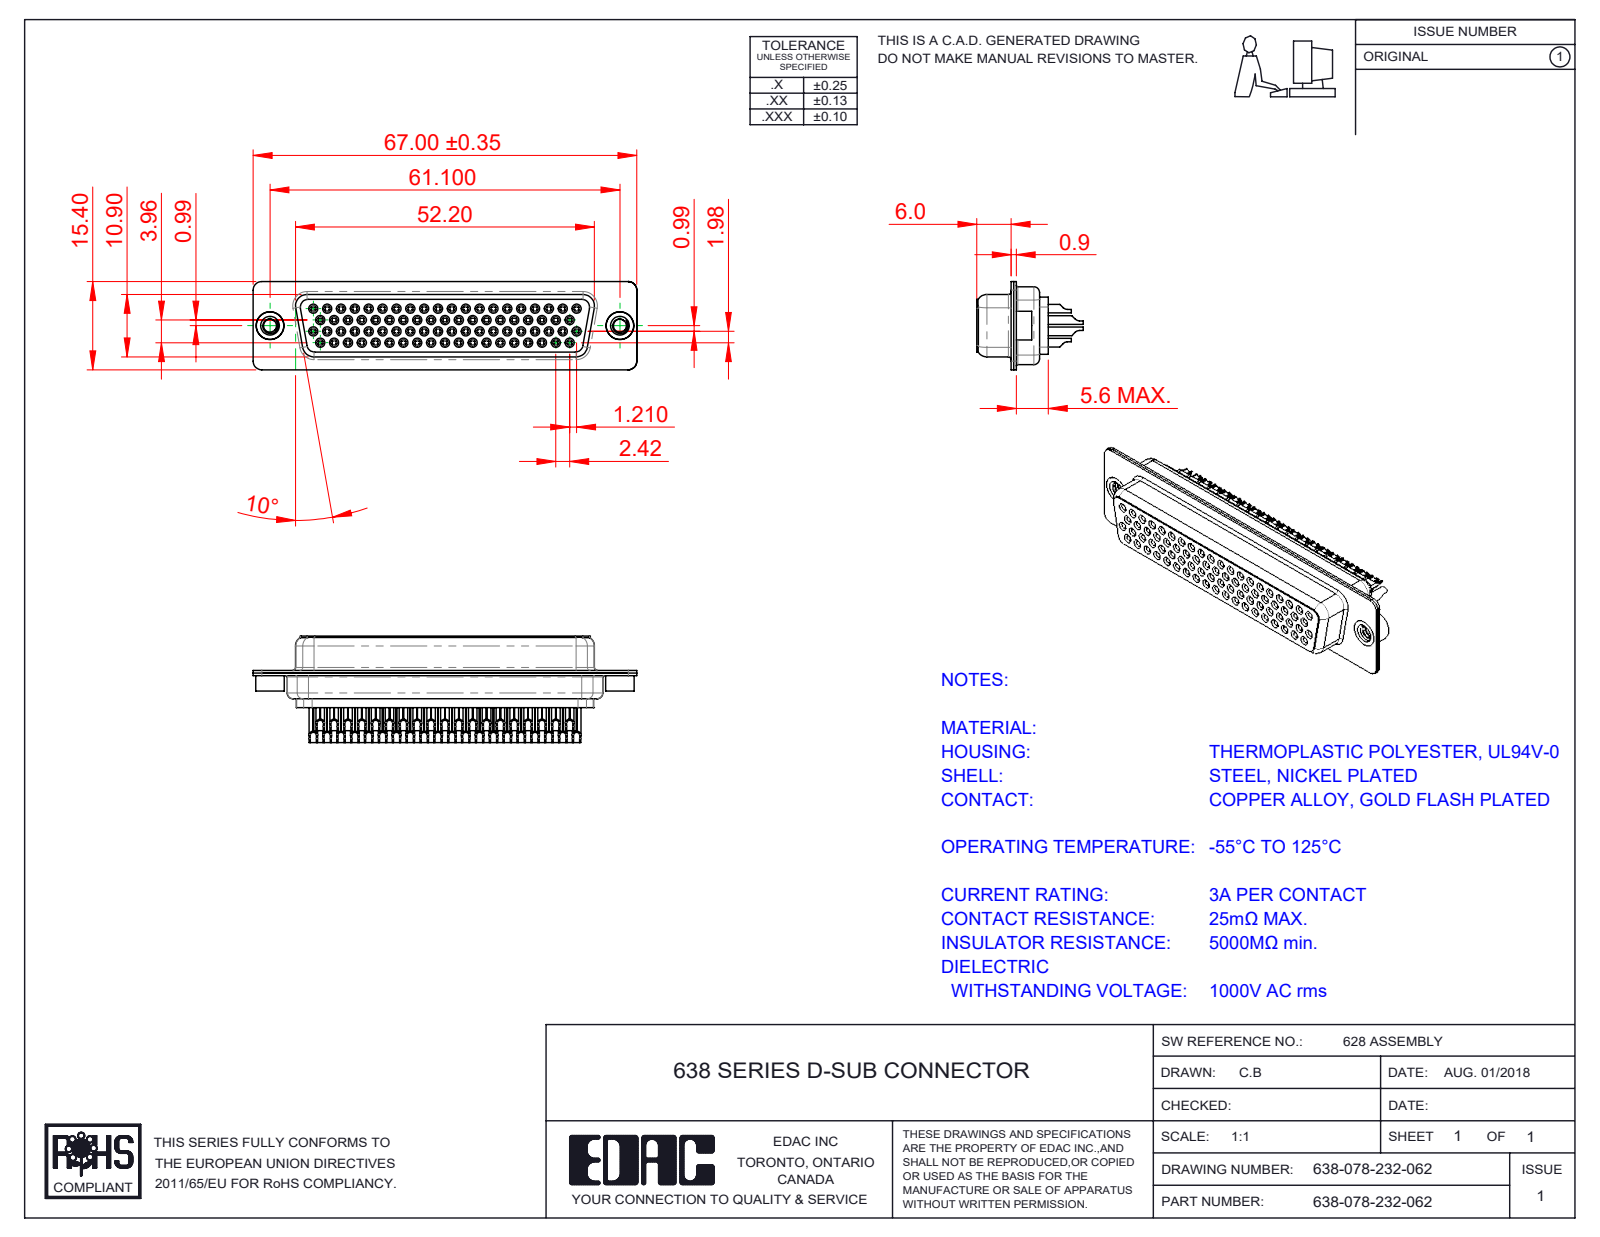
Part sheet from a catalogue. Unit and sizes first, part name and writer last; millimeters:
Units: millimetres
Overall size (bounding box): 67 × 18.6 × 15.4
Round holes (diameter × count): ⌀0.8 ×78, ⌀1 ×78, ⌀1.1 ×78, ⌀1.6 ×78, ⌀1.7 ×78, ⌀1.8 ×78, ⌀2.26 ×2, ⌀4 ×2, ⌀4.05 ×2, ⌀4.85 ×2
Round bosses / shafts (diameter × count): ⌀2 ×78, ⌀1.5 ×78, ⌀1.2 ×78, ⌀5 ×2, ⌀4.95 ×2, ⌀4.8 ×2, ⌀4 ×1
Partial cylindrical surfaces — rounded edges, fillets, slot ends (radius × count): R0.28 ×39, R1.5 ×16, R2 ×12, R1 ×8, R1.55 ×8, R0.25 ×4, R0.5 ×4, R0.55 ×4
Main face-to-face distances: 0.45, 0.4, 0.9, 1.35, 9.6, 11.8, 1.8, 11.4, 2.2, 13.15
Hole centre spacings: 2.42, 4.84, 7.26, 9.68, 6.06, 12.1, 6.96, 8.48
Volume: 6 040 mm³ · Surface area: 22 123 mm²
Bodies: 83 solids, 7221 faces (1705 planar, 2087 cylindrical, 3429 other)
Part name (STEP PRODUCT): 638 Contact Row 1_32(78); 638-078-232-062; 638 Contact Row 78_32; 638 Contact Row 2_32(78) (+5 more)
STEP written by: SolidWorks 2020 (CONFIG_CONTROL_DESIGN)
